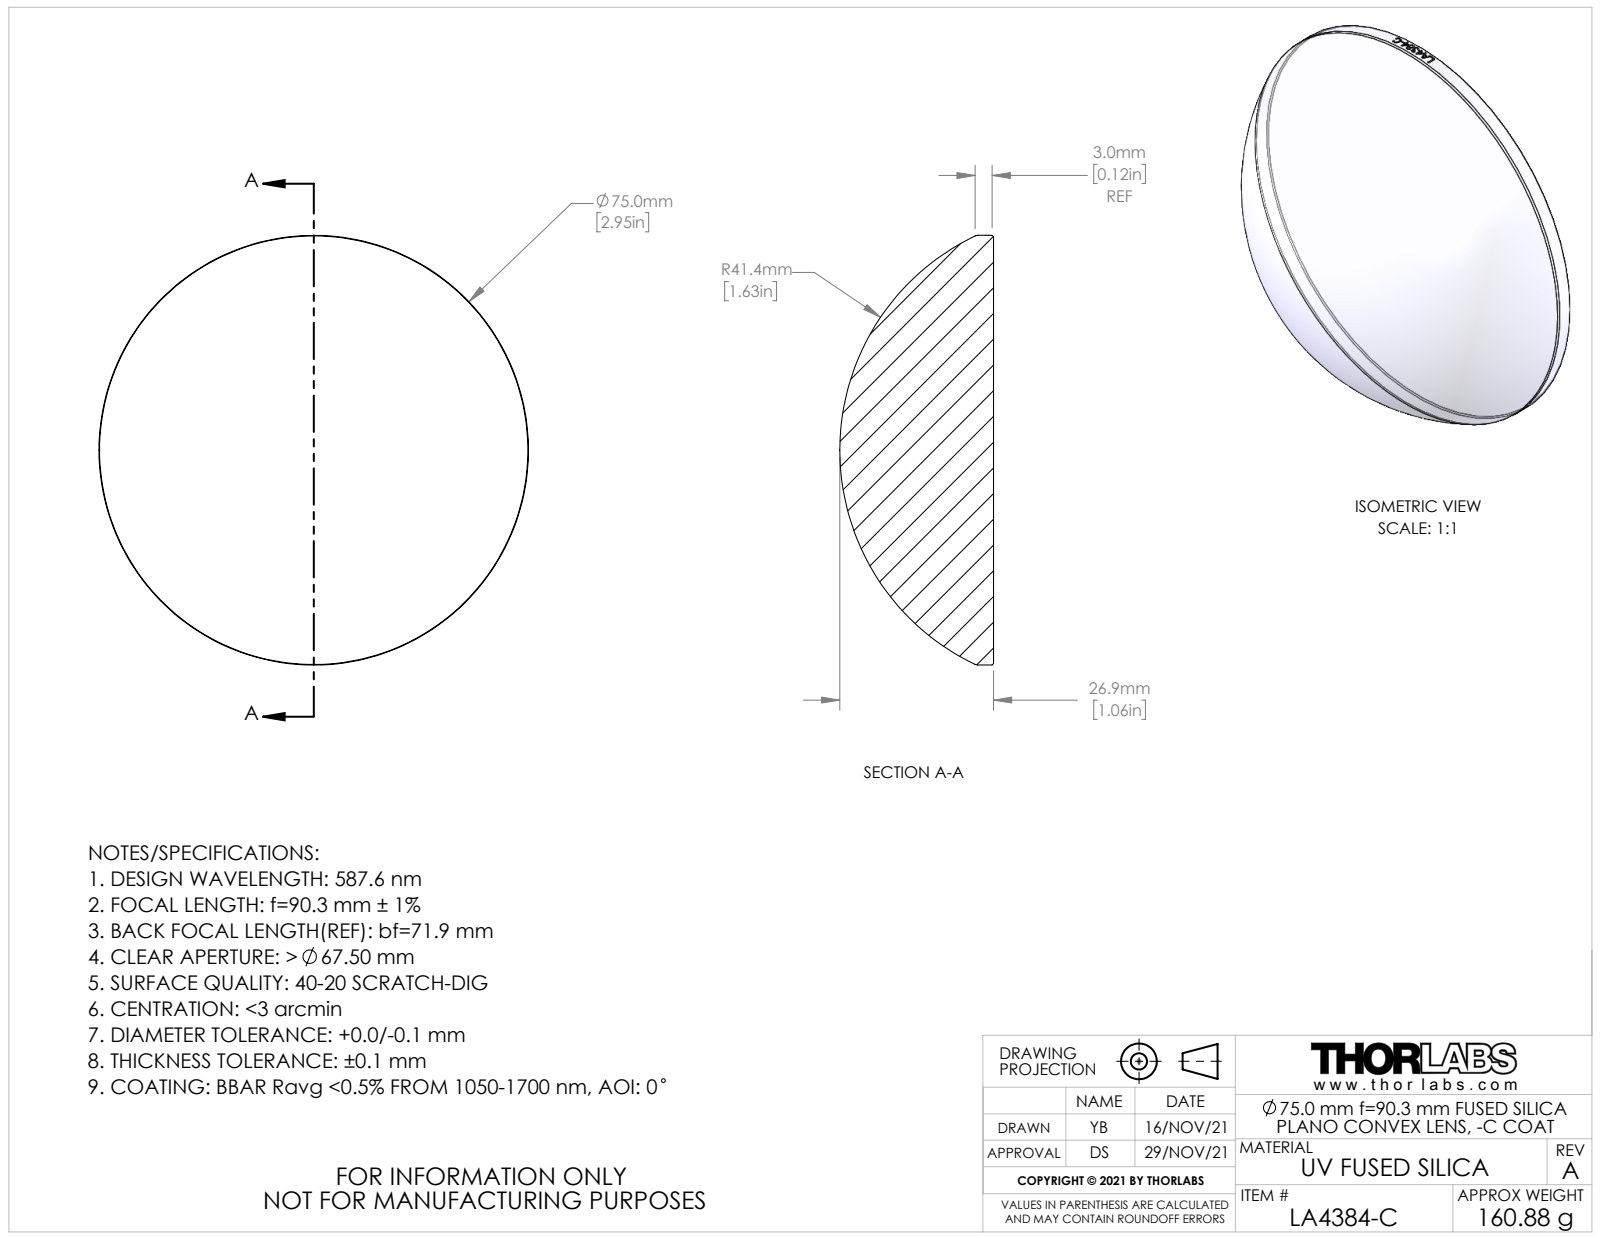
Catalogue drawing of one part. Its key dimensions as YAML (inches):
part_name: "CTN018151; CTN018085-E0W"
step_written_by: "SolidWorks 2018 (AUTOMOTIVE_DESIGN)"
units: inches
bodies: {solids: 1, faces: 22, planar: 1, cylindrical: 15, other: 6}
overall_size: [2.953, 2.953, 1.057]
volume: 4.456
surface_area: 17.5
round_bosses_or_shafts:
  - {diameter: 2.953, count: 1}
